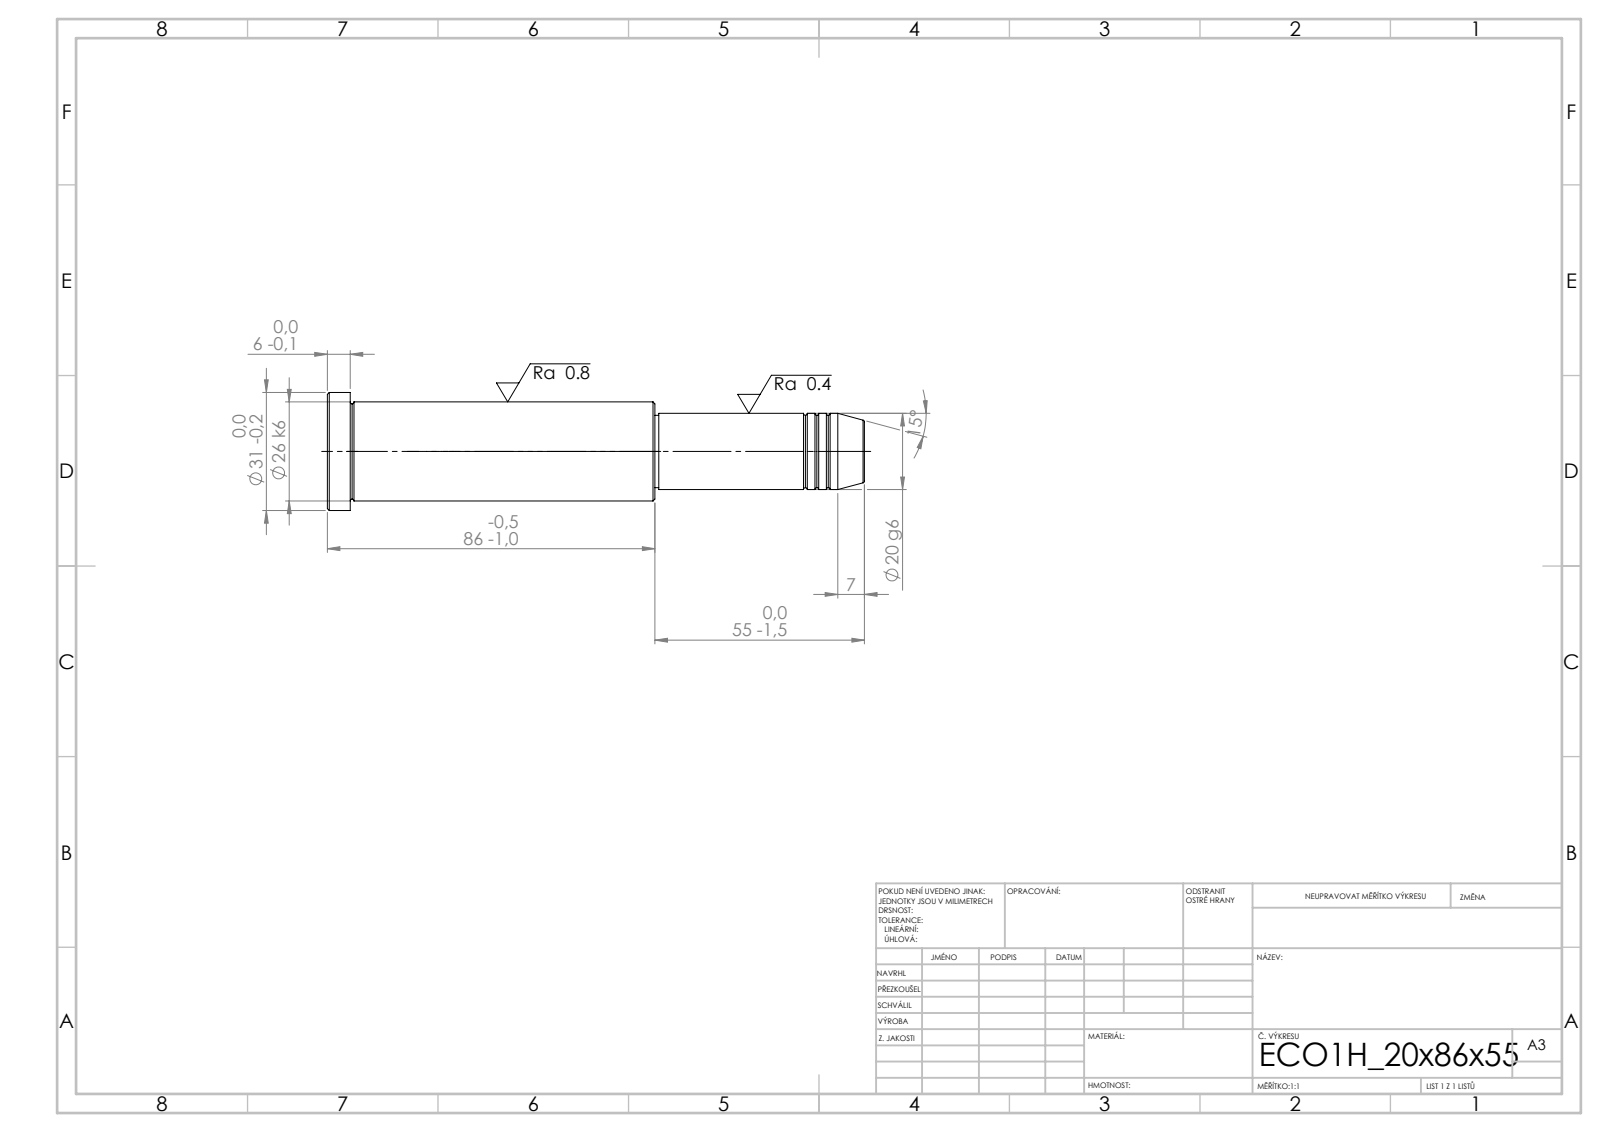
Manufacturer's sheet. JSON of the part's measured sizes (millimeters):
{"step_written_by": "SolidWorks 2019 (CONFIG_CONTROL_DESIGN)", "units": "millimeters", "bodies": {"solids": 1, "faces": 43, "planar": 5, "cylindrical": 14, "other": 24}, "overall_size": [141, 31, 31], "volume_mm3": 63737, "surface_area_mm2": 12091, "round_bosses_or_shafts": [[31, 1], [26, 1], [20, 1], [19, 1]], "face_to_face_distances": [6, 80, 86, 55, 135, 141, 54, 1, 81, 87]}
